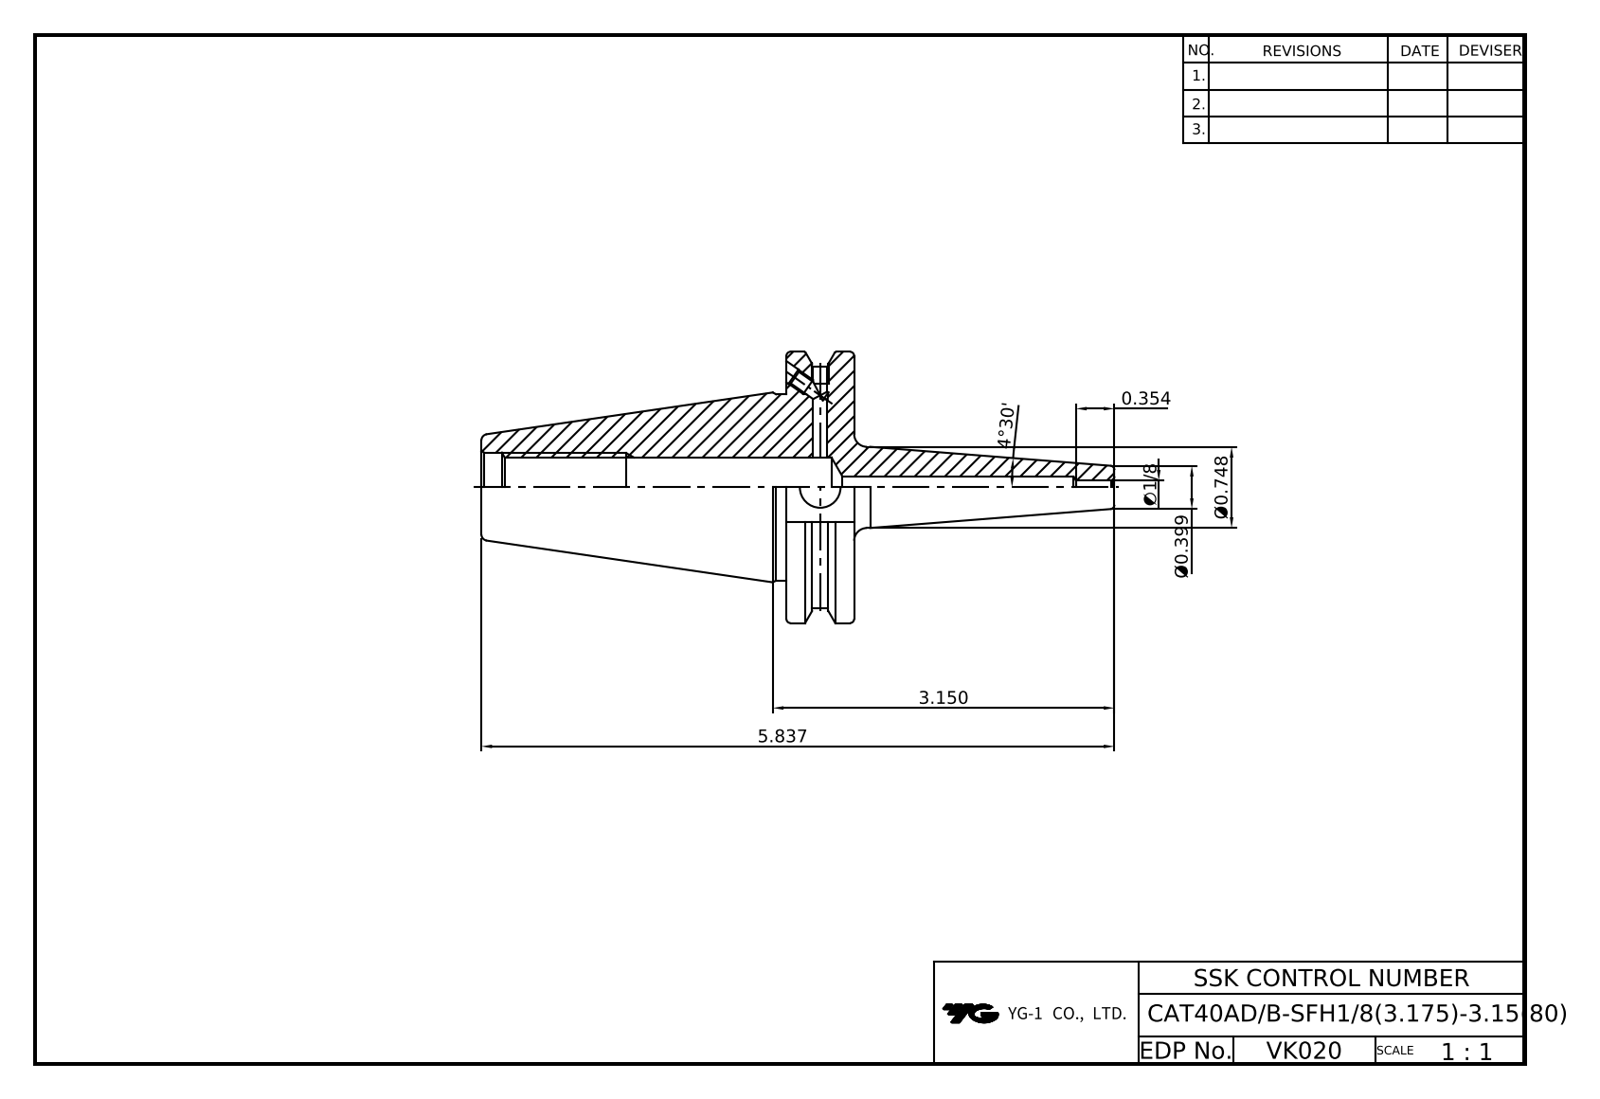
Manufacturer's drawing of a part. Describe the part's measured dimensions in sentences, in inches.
The part is named "LO-CAT40ADB-SFH3.175-80". Its 3-D file was written by "Autodesk Inventor 2022 (AUTOMOTIVE_DESIGN)". It is 1 solid with 85 faces: 35 planar, 28 cylindrical and 22 other. Overall it measures 5.837 by 2.5 by 2.405 inches. Its volume is 6.779 cubic inches and its surface area 37.49 square inches. Round holes: 4 of diameter 0.128, 2 of diameter 0.157, 2 of diameter 0.165, 1 of diameter 0.125, 1 of diameter 0.197, 1 of diameter 0.375, 1 of diameter 0.512, 1 of diameter 0.527, 1 of diameter 0.642. Round bosses or shafts: 1 of diameter 2.5, 1 of diameter 1.717, 1 of diameter 0.748. Partial cylindrical surfaces (rounded edges, fillets, slot ends): 1 of radius 1.108. The main face-to-face distances are 0.625, 1.874, 0.645, 2.812, 3.437, 3.05, 0.238, 0.387, 3.201, 0.389.
